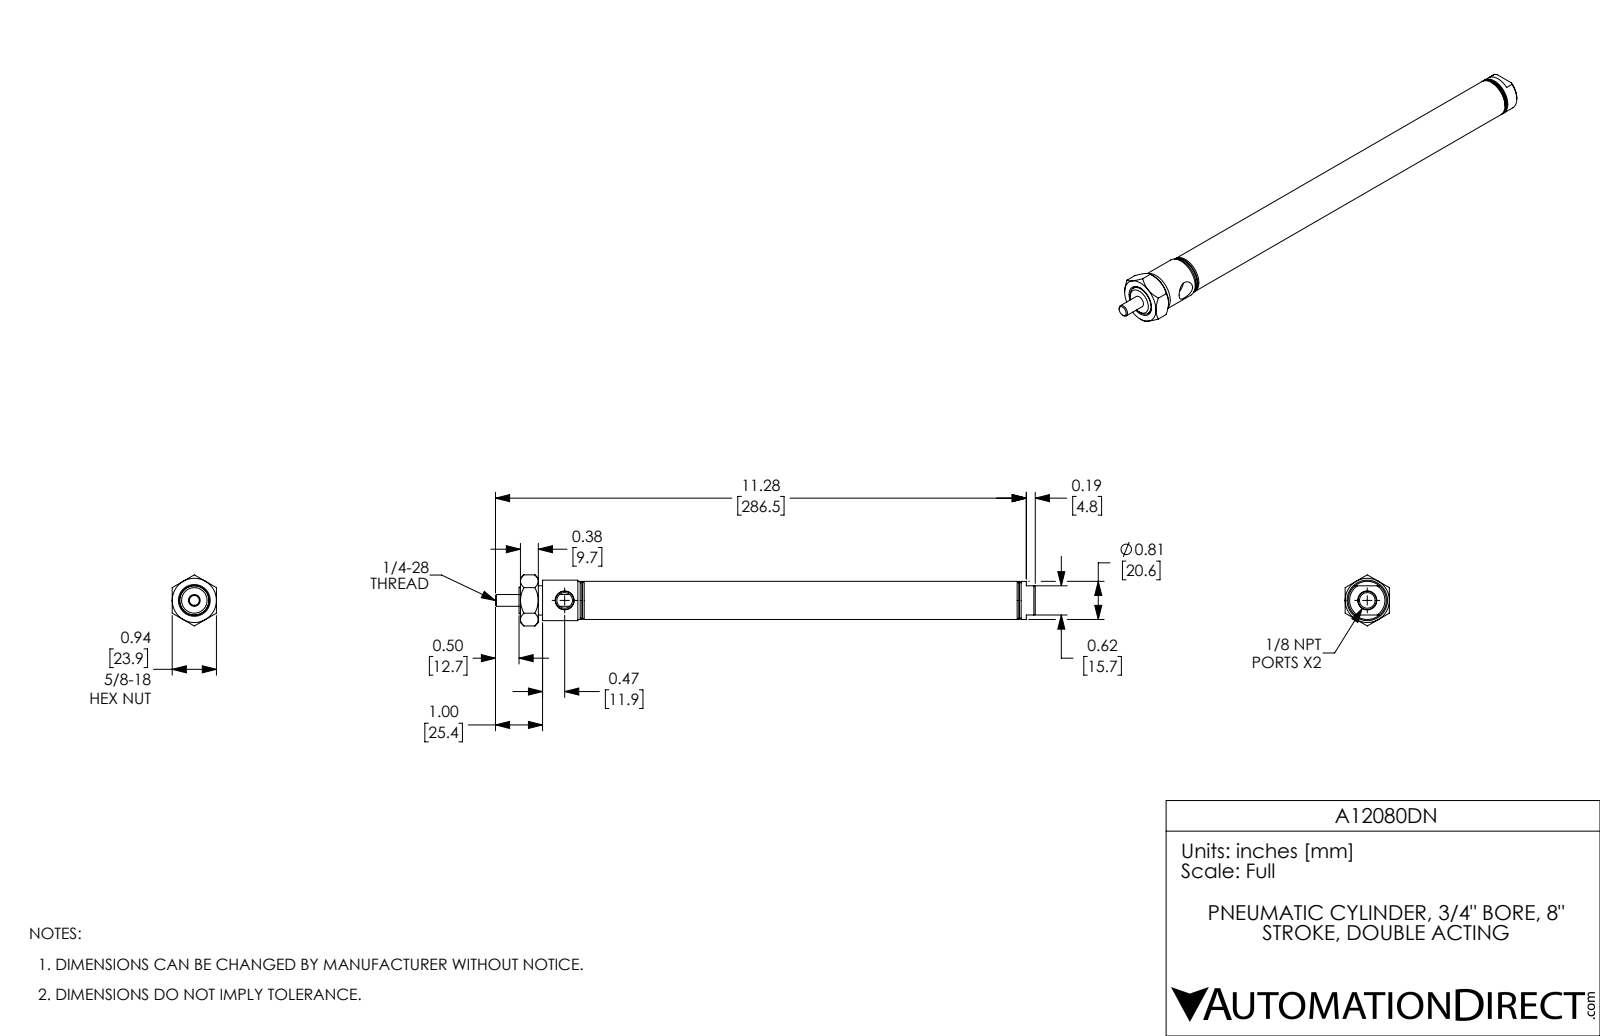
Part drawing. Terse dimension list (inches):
name: A12080DN_Mounting Nut_D-9; A12080DN-Rod; A12080DN-MainBody; A12080DN
written by: SolidWorks 2017 (AUTOMOTIVE_DESIGN)
unit: in
bodies: 3 solids, 94 faces (27 planar, 28 cylindrical, 39 other)
size: 11.47 × 1.085 × 0.94
volume: 2.494 in³; area: 65.01 in²
holes: 2× ⌀0.332, 1× ⌀0.25, 1× ⌀0.625, 1× ⌀0.75
bosses: 1× ⌀0.86, 1× ⌀0.81, 1× ⌀0.623
face distances: 9.485, 0.94, 0.5, 0.985, 1.485, 8.5, 8, 9.575, 9.075, 1.075
